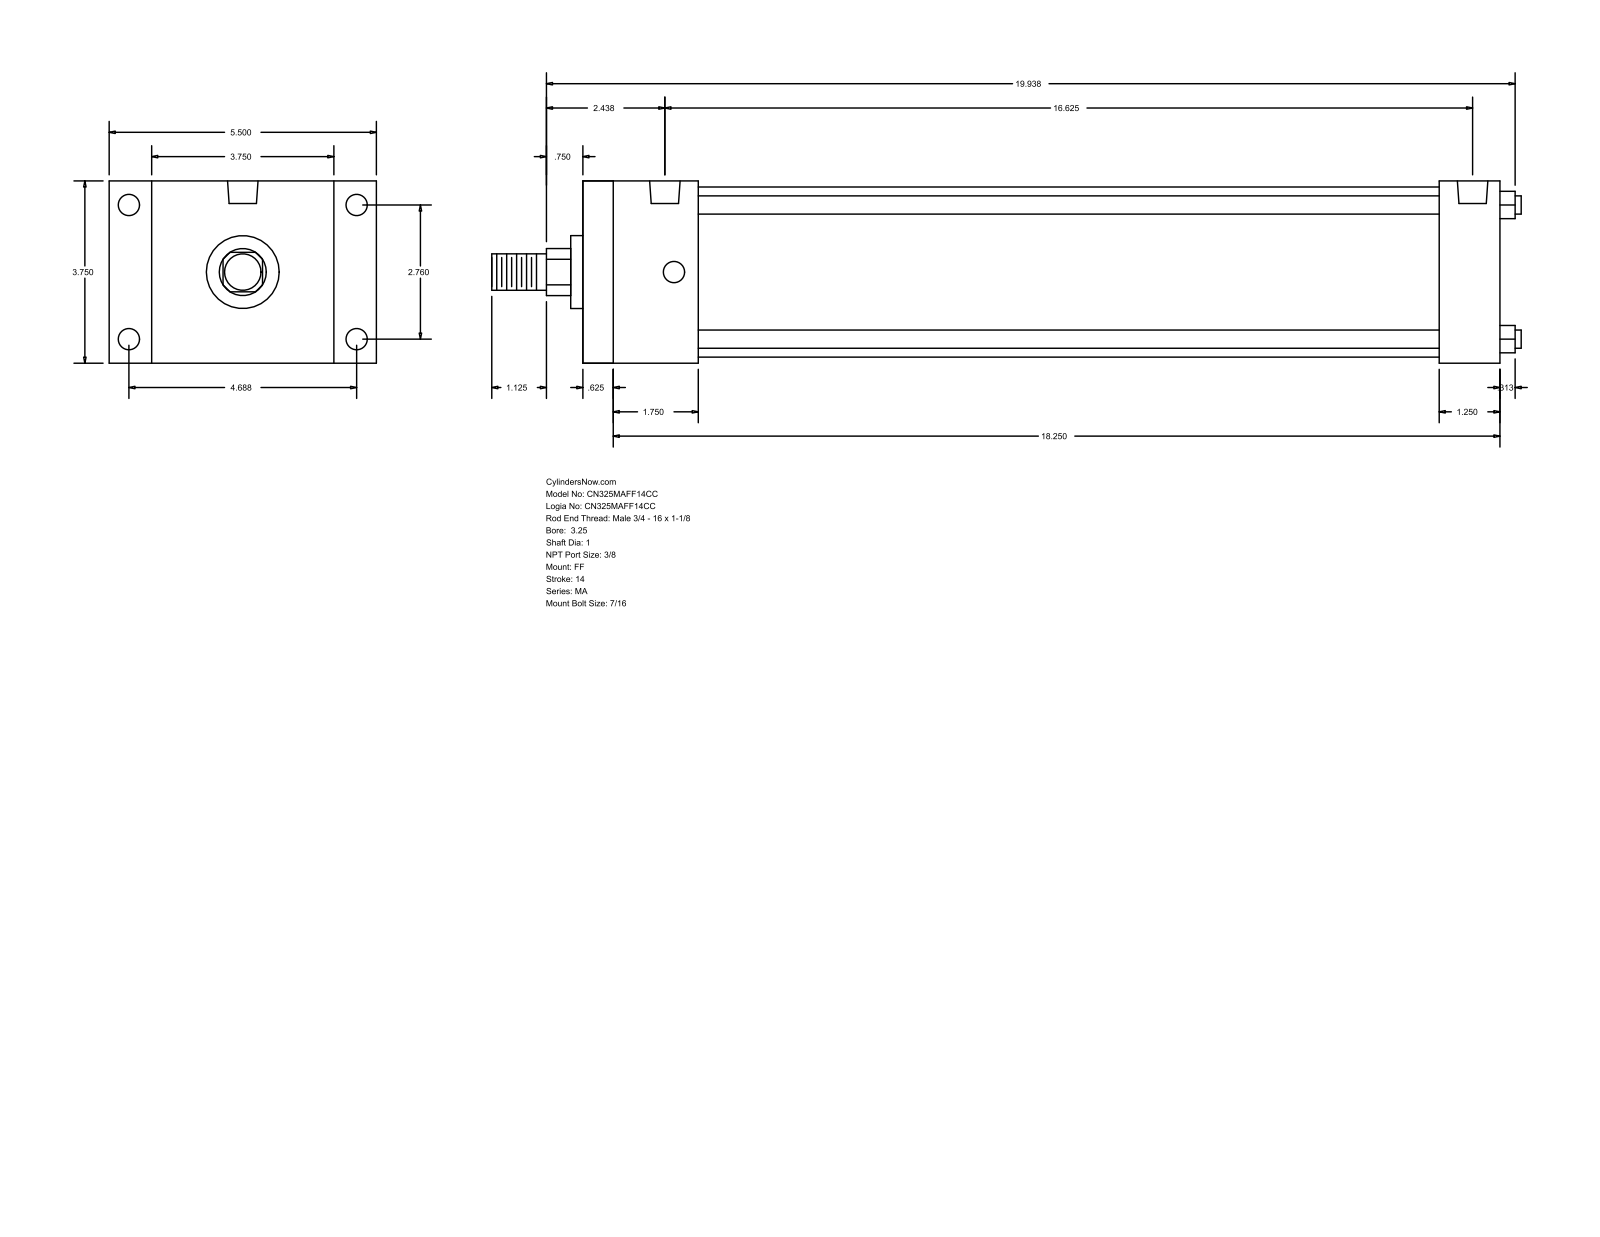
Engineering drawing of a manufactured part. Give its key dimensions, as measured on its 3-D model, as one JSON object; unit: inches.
{"part_name": "MA_FF__0325_1", "step_written_by": "GSSL Pune (CONFIG_CONTROL_DESIGN)", "units": "inches", "bodies": {"solids": 0, "faces": 92, "planar": 64, "cylindrical": 28, "other": 0}, "overall_size": [21.187, 5.5, 3.75], "round_holes": [[0.437, 8], [0.627, 2]], "round_bosses_or_shafts": [[0.375, 4], [3.5, 1], [1.5, 1], [1, 1], [0.75, 1]], "partial_cylinders_radius": [[0.484, 1]], "face_to_face_distances": [3.75, 18.875, 0.625, 18.25, 0.875, 4.625, 2.375, 17.625, 1.75, 17], "hole_center_spacings": [0.187, 2.76, 4.687, 5.439, 16.25, 16.438, 16.625]}
